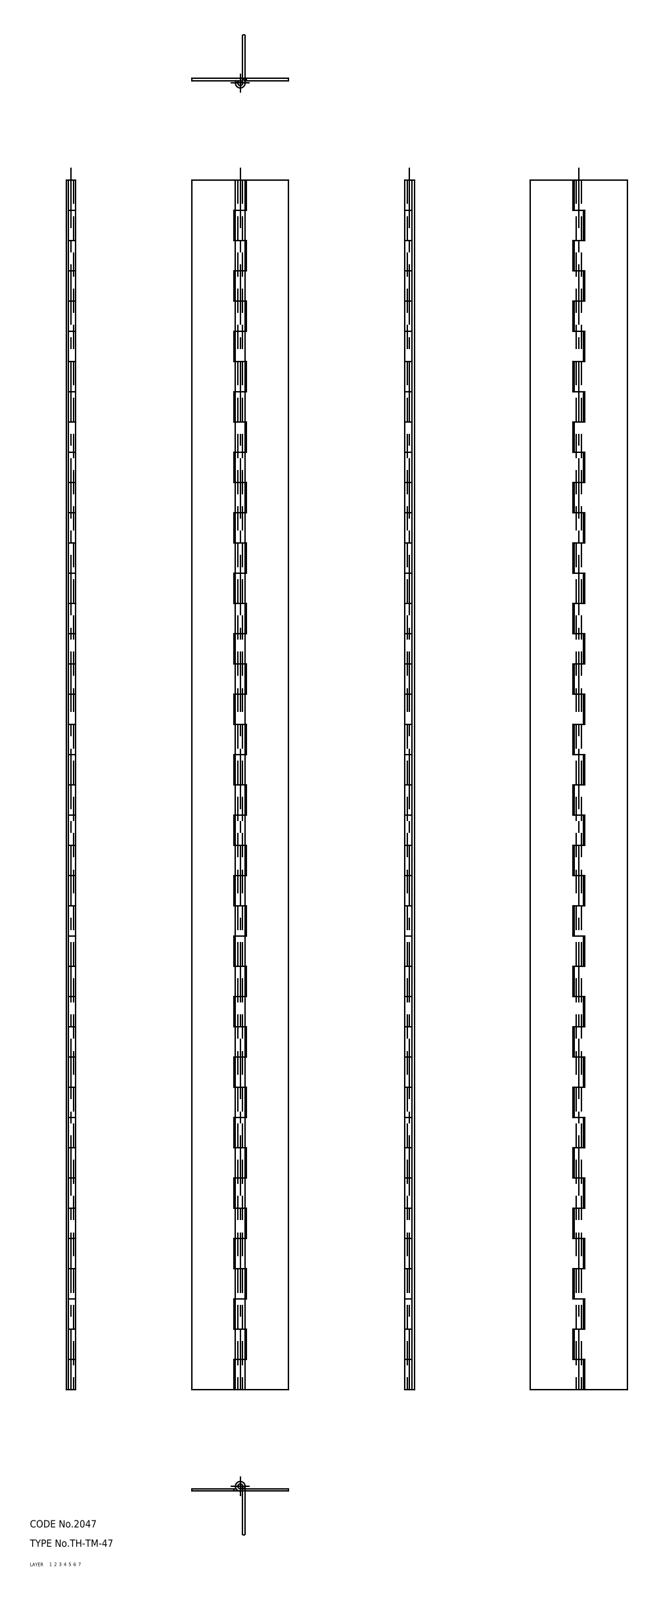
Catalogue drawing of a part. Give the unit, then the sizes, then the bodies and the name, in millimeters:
Units: millimetres
Overall size (bounding box): 500 × 40 × 4
Volume: 24 229 mm³ · Surface area: 51 357 mm²
Bodies: 3 solids, 252 faces (0 planar, 0 cylindrical, 252 other)
Part name (STEP PRODUCT): hinge piece_B; hinge piece_A; shaft; TH_TM_47_23590_36
STEP written by: CADfix (AUTOMOTIVE_DESIGN)
